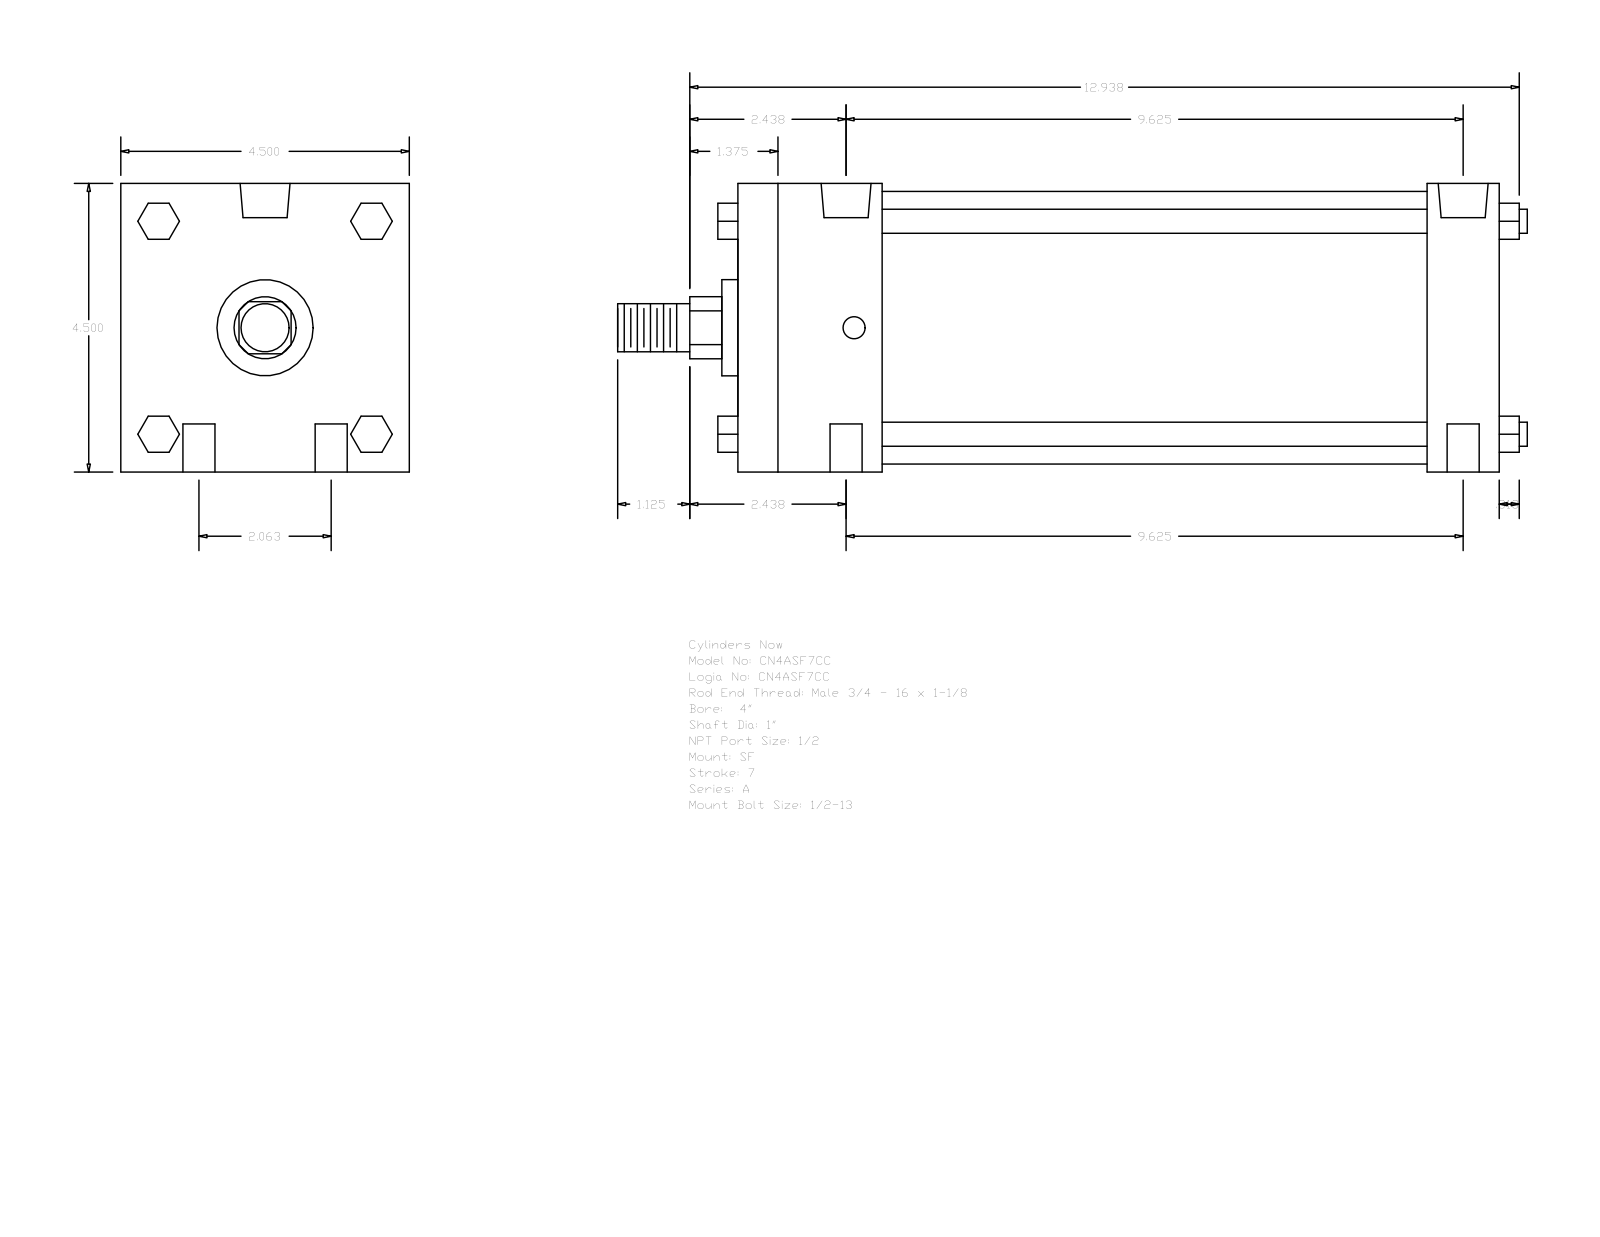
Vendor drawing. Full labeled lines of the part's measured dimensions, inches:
Part name (STEP PRODUCT): A_SF__0400_1
STEP written by: GSSL Pune (CONFIG_CONTROL_DESIGN)
Units: inches
Bodies: 0 solids, 124 faces (94 planar, 30 cylindrical, 0 other)
Overall size (bounding box): 14.187 × 4.5 × 4.5
Round holes (diameter × count): ⌀0.5 ×4, ⌀0.344 ×2, ⌀0.778 ×2
Round bosses / shafts (diameter × count): ⌀0.375 ×4, ⌀4.25 ×1, ⌀1.5 ×1, ⌀1 ×1, ⌀0.75 ×1
Partial cylindrical surfaces — rounded edges, fillets, slot ends (radius × count): R0.484 ×1
Main face-to-face distances: 4.5, 11.875, 10.75, 1.125, 2.25, 8.5, 9.625, 0.563, 1.66, 2.875
Hole centre spacings: 1.031, 9.68, 9.625, 2.062, 9.844, 9.375
